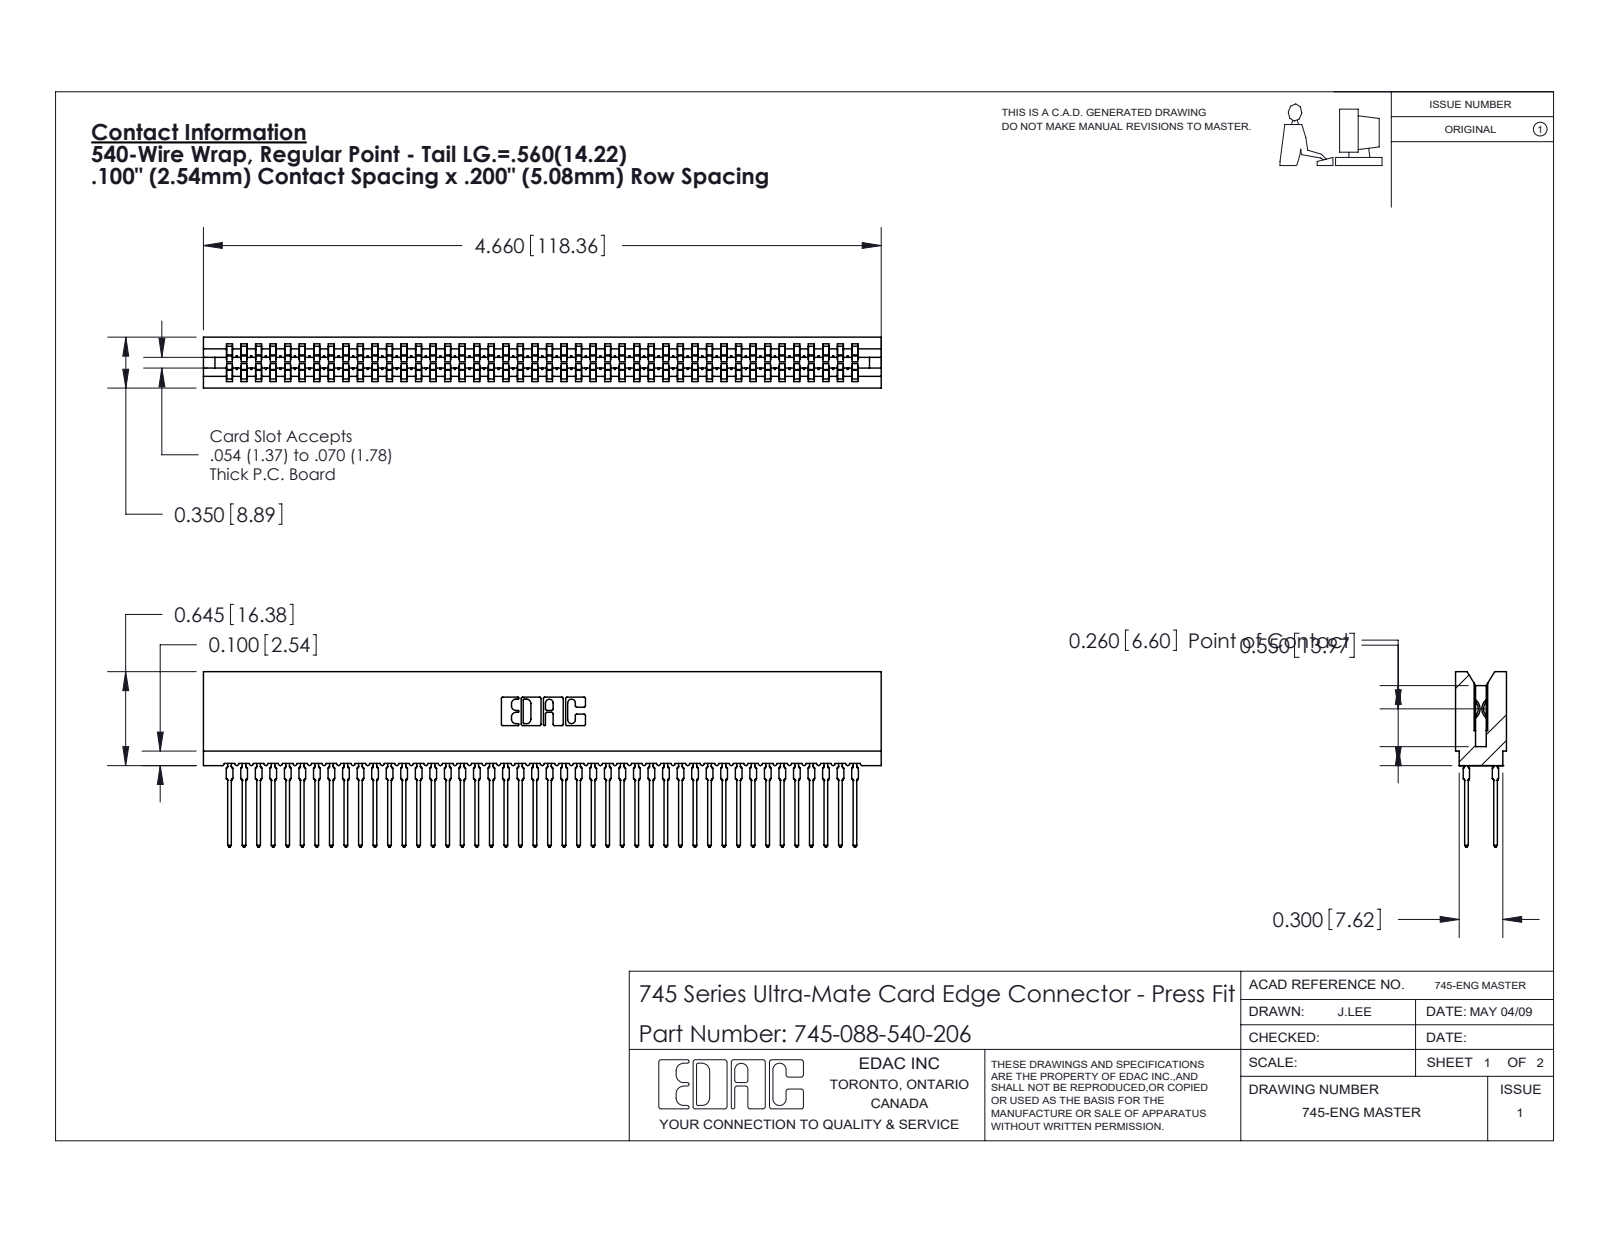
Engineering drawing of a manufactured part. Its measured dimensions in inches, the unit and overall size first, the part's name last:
Units: inches
Overall size (bounding box): 4.66 × 1.206 × 0.35
Partial cylindrical surfaces — rounded edges, fillets, slot ends (radius × count): R0.021 ×176, R0.015 ×88, R0.01 ×22, R0.005 ×8, R0.011 ×8, R0.007 ×6, R0.031 ×6, R0.026 ×3
Main face-to-face distances: 0.063, 0.287, 0.2, 0.35, 0.045, 0.305, 0.018, 0.243, 0.138, 0.212
Volume: 0.664 in³ · Surface area: 35.99 in²
Bodies: 89 solids, 7972 faces (4104 planar, 1580 cylindrical, 2288 other)
Part name (STEP PRODUCT): 745-088-540-206; 745 Part_Insulator Option - 06; 745-292-001_540
STEP written by: SolidWorks 2020 (CONFIG_CONTROL_DESIGN)
